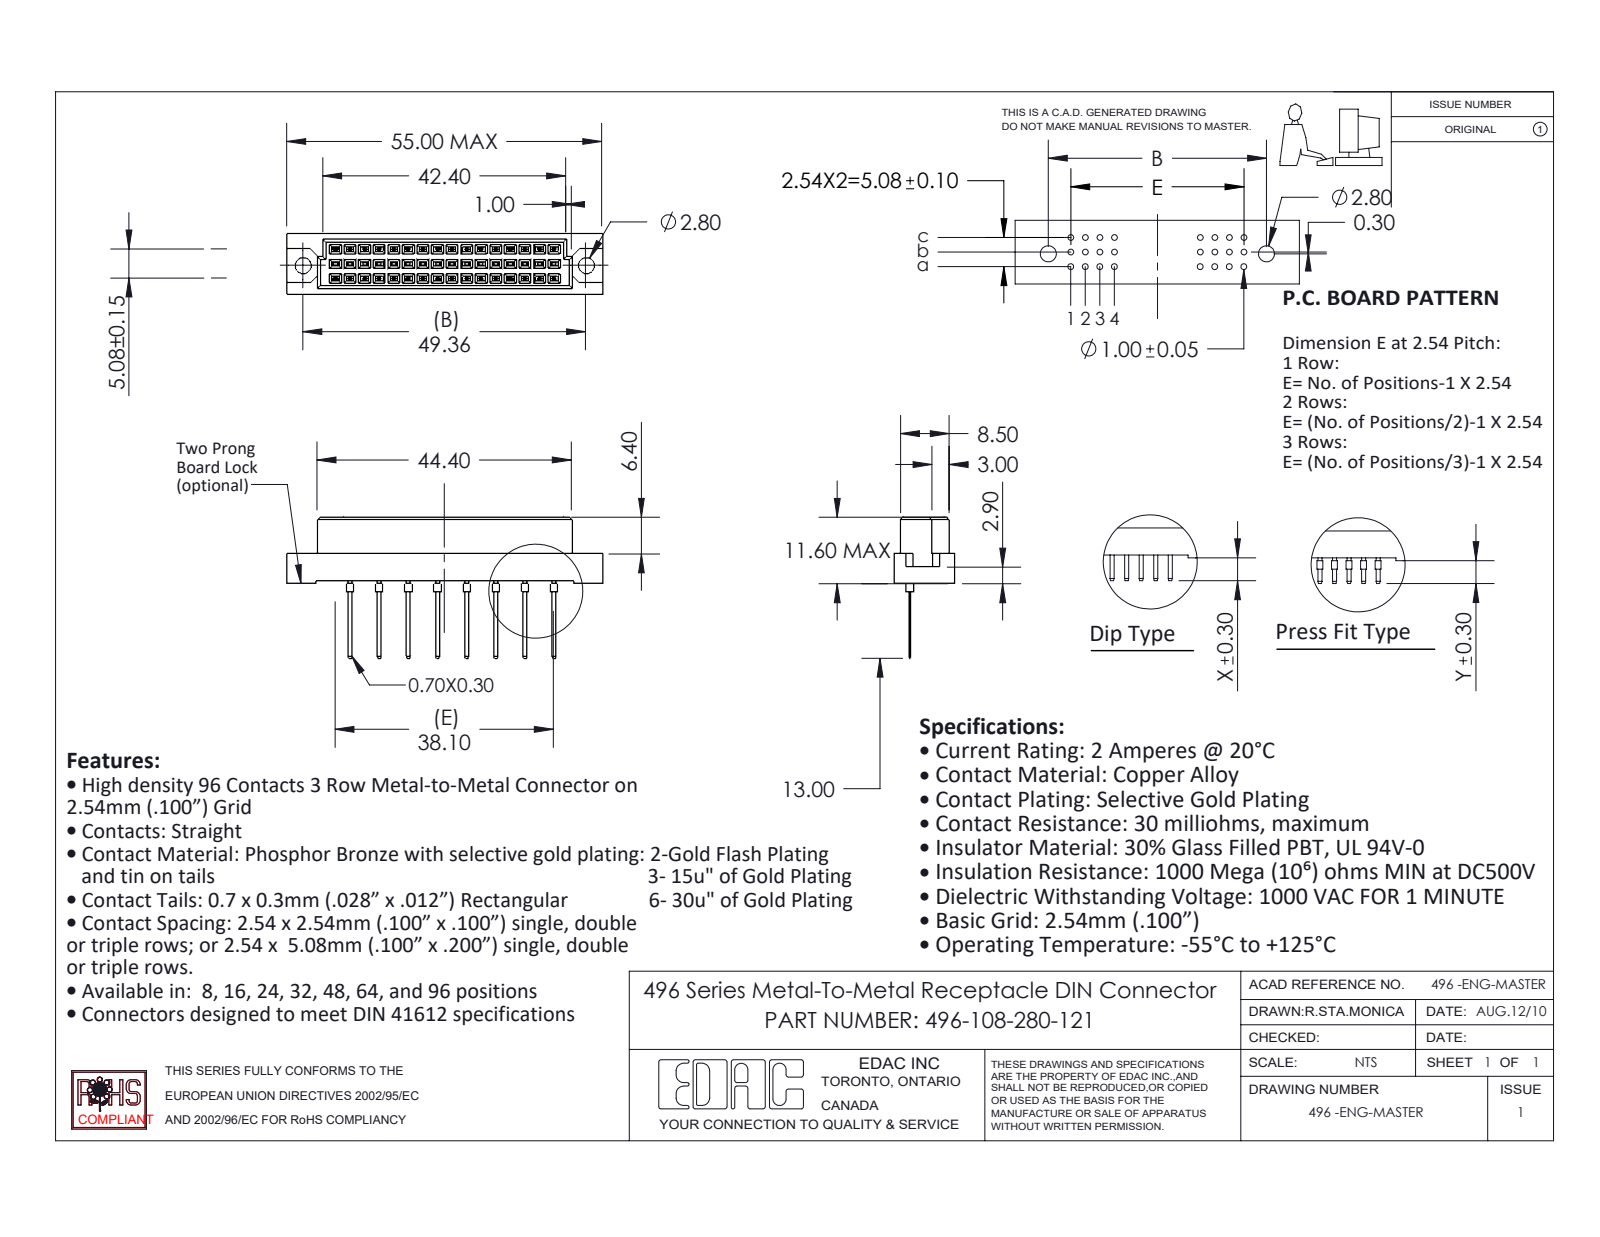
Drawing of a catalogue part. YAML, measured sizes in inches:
part_name: "496-108-280-121; 496-290_80; 496 Part_48"
step_written_by: "SolidWorks 2020 (CONFIG_CONTROL_DESIGN)"
units: inches
bodies: {solids: 9, faces: 810, planar: 790, cylindrical: 20, other: 0}
overall_size: [2.165, 0.969, 0.417]
volume: 0.282
surface_area: 7.012
round_holes:
  - {diameter: 0.11, count: 2}
round_bosses_or_shafts:
  - {diameter: 0.039, count: 8}
face_to_face_distances: [0.1, 0.2, 0.041, 0.376, 0.032, 0.417, 0.132, 0.068, 0.335, 0.022]
hole_center_spacings: [1.943]
